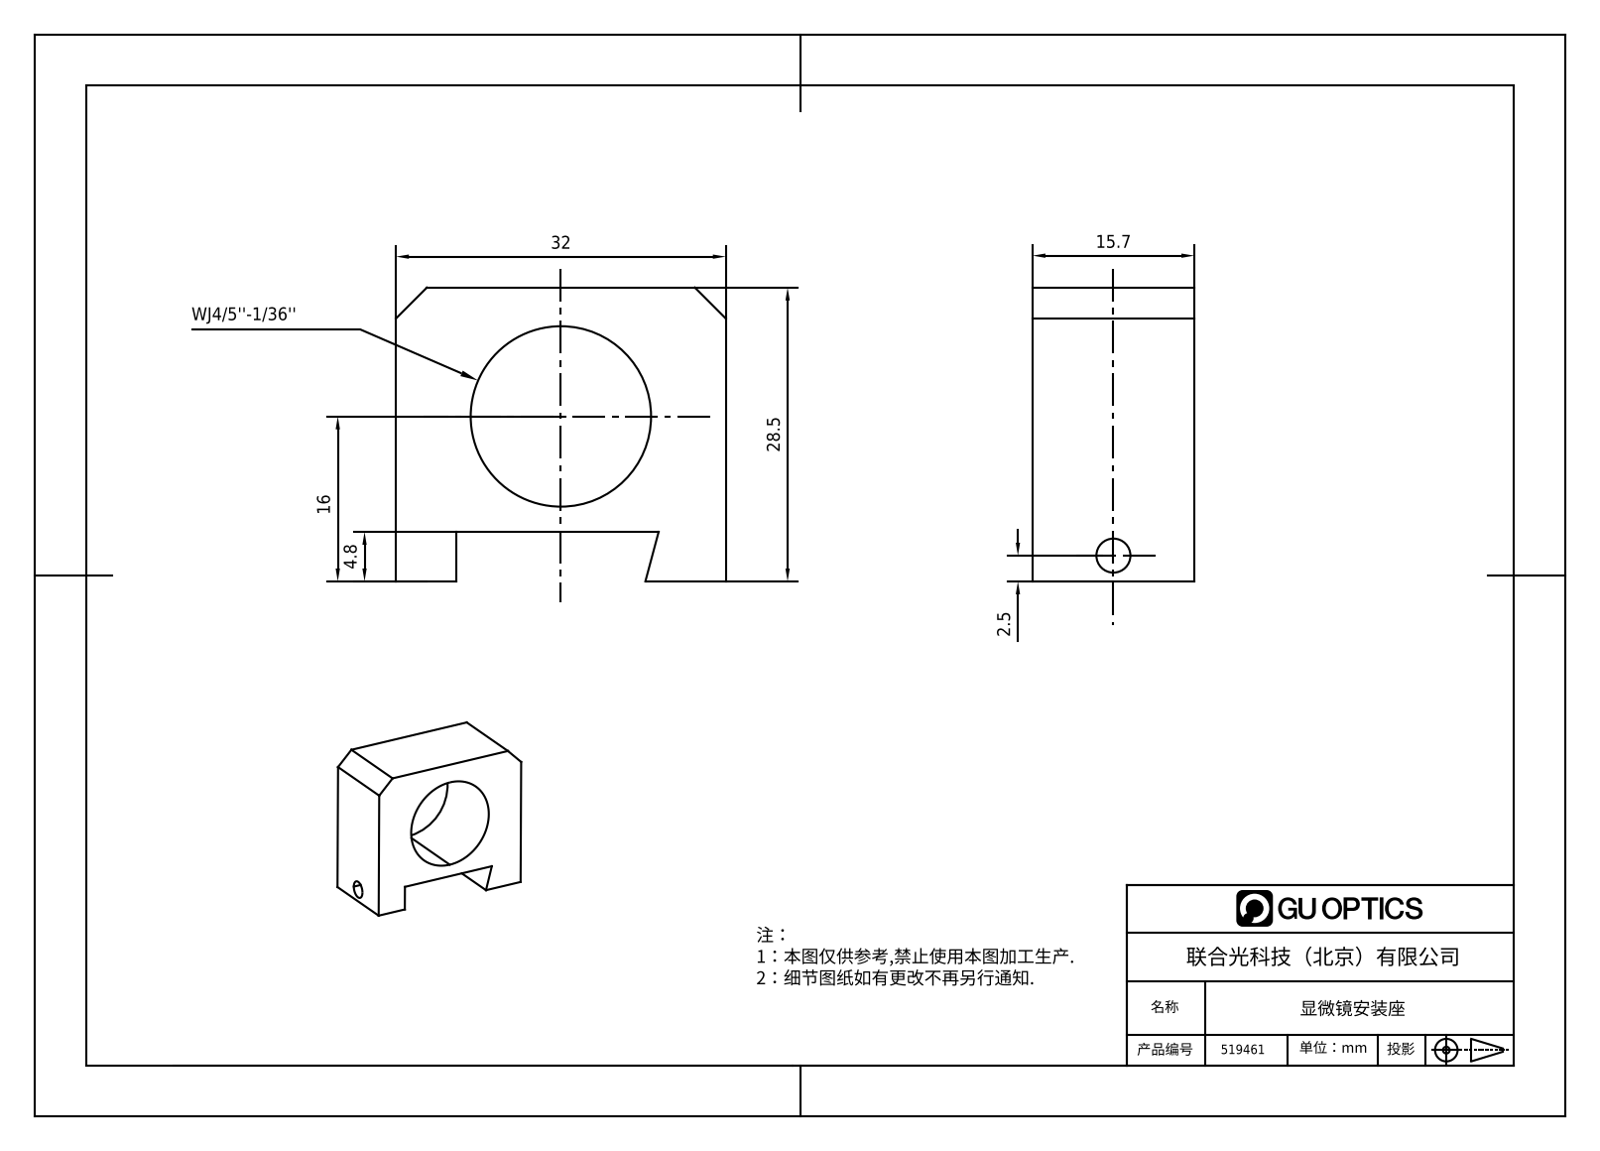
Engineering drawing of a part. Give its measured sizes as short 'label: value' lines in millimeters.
name: MF-OM
written by: SolidWorks 2016 (CONFIG_CONTROL_DESIGN)
unit: mm
bodies: 1 solid, 16 faces (12 planar, 4 cylindrical, 0 other)
size: 32 × 28.5 × 15.7
volume: 8 923 mm³; area: 4 068 mm²
holes: 1× ⌀3.3, 1× ⌀17.5
face distances: 15.7, 32, 23.7, 28.5, 4.8, 5.9, 26.1
